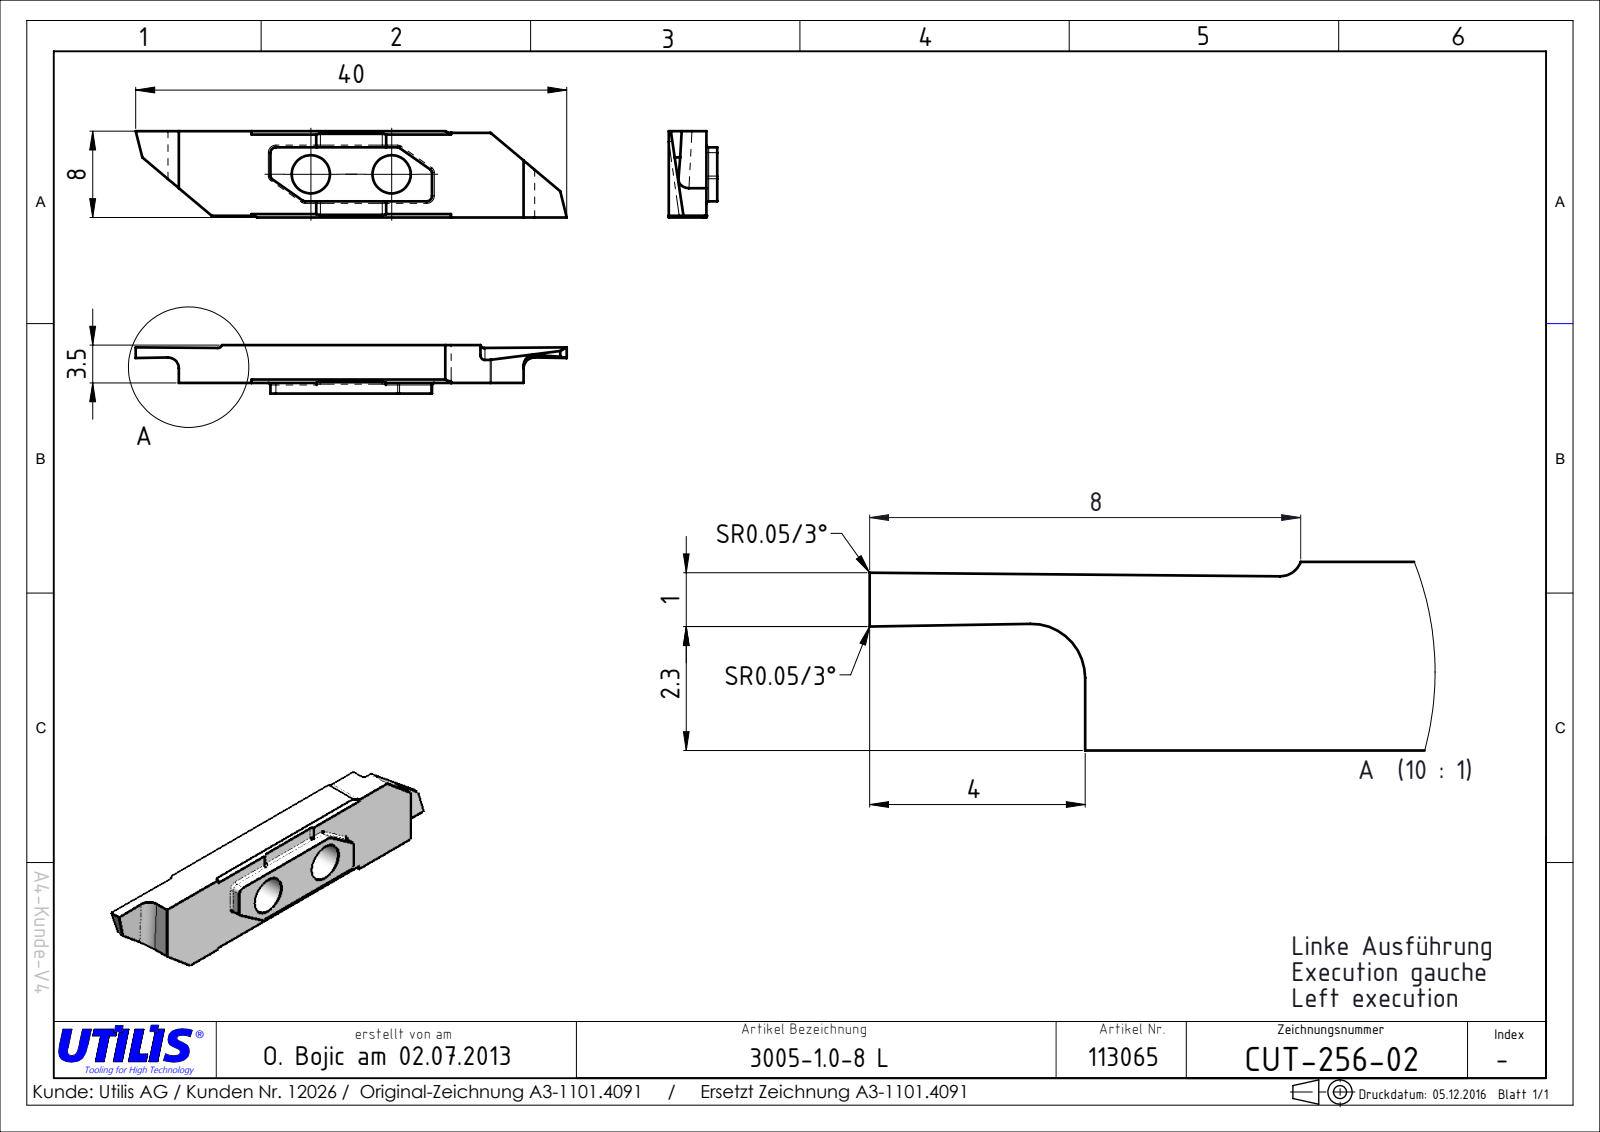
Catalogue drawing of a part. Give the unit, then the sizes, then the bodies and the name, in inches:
Units: inches
Overall size (bounding box): 1.575 × 0.315 × 0.138
Round holes (diameter × count): ⌀0.14 ×2
Partial cylindrical surfaces — rounded edges, fillets, slot ends (radius × count): R0.006 ×4, R0.039 ×4, R0.016 ×2
Main face-to-face distances: 0.138, 0.315, 0.309, 0.887, 0.303, 1.26, 0.157, 1.417, 1.575, 1.535
Hole centre spacings: 0.295
Volume: 0.049 in³ · Surface area: 1.32 in²
Bodies: 1 solid, 38 faces (24 planar, 14 cylindrical, 0 other)
Part name (STEP PRODUCT): CUT-256-02
STEP written by: SolidWorks 2016 (AUTOMOTIVE_DESIGN)
